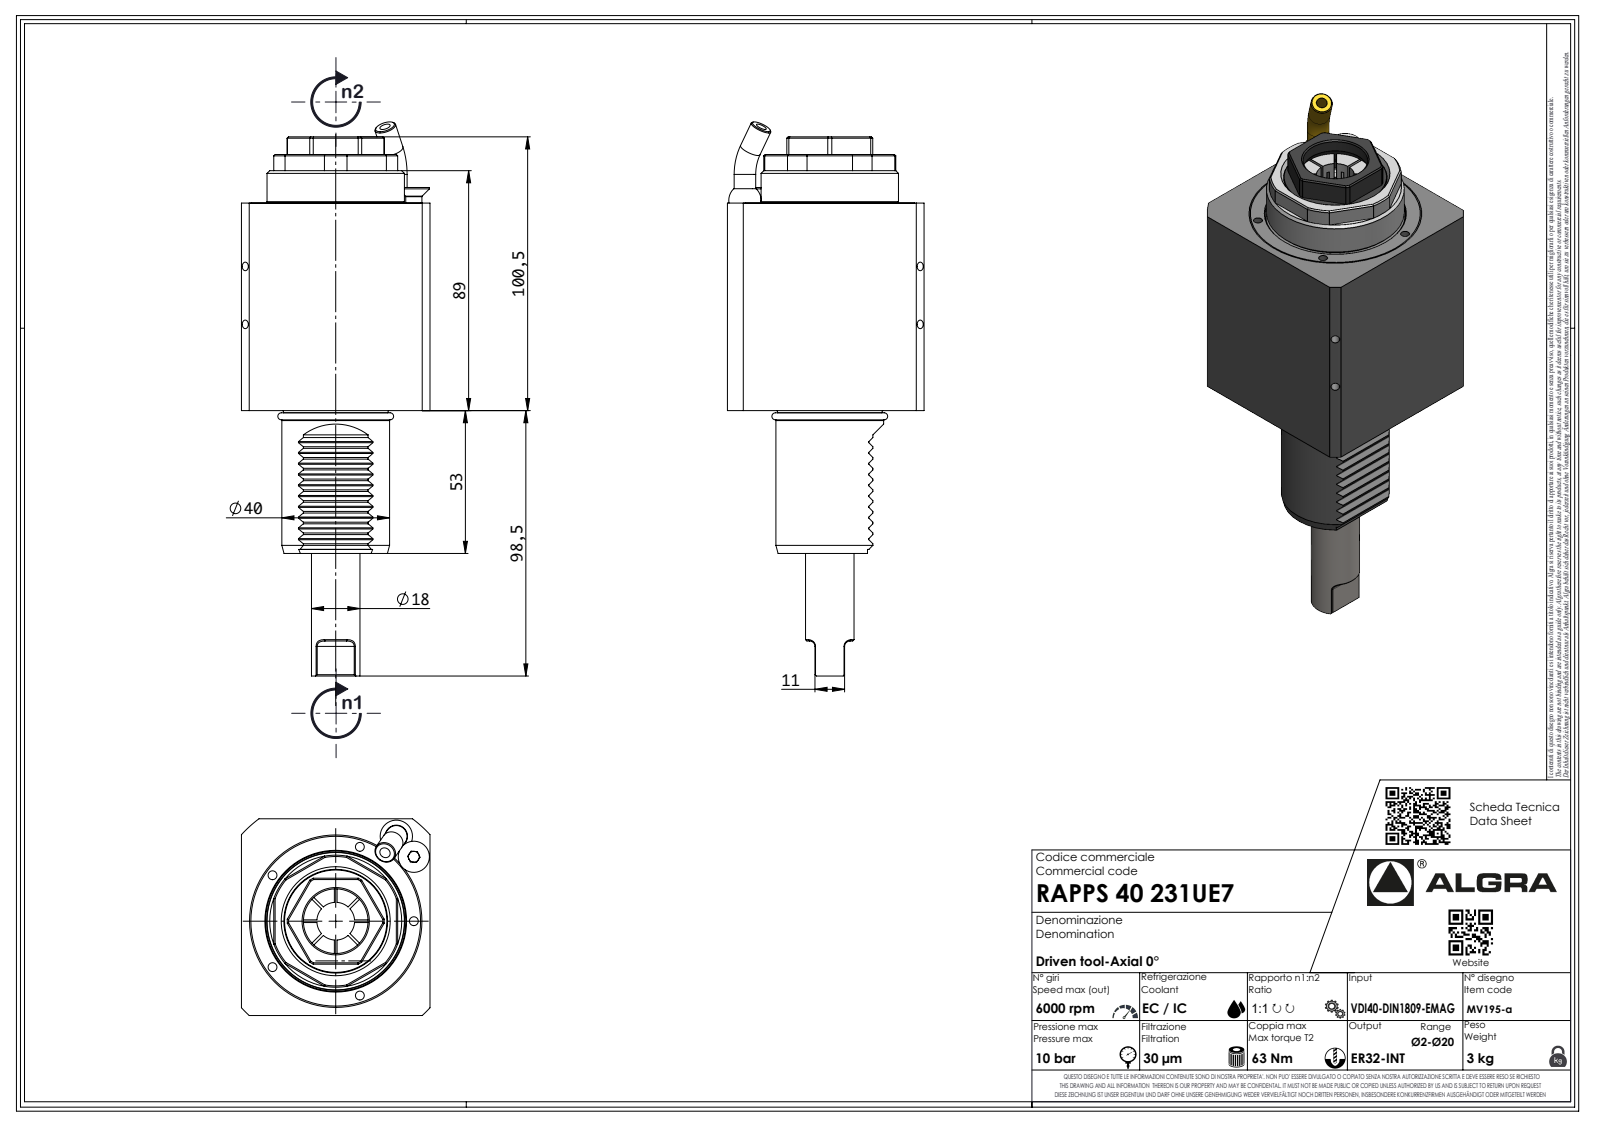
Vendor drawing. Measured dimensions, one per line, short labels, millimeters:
name: RAPPS40231UE7
written by: SolidWorks 2023 (AUTOMOTIVE_DESIGN)
unit: mm
bodies: 1 solid, 446 faces (285 planar, 61 cylindrical, 100 other)
size: 205.6 × 73 × 70
volume: 505 574 mm³; area: 44 996 mm²
holes: 1× ⌀2.1
bosses: 2× ⌀8, 1× ⌀51, 1× ⌀40, 1× ⌀38.7, 1× ⌀18, 1× ⌀6.37, 1× ⌀1.7
rounds: 11× R0.3, 7× R0.33, 7× R0.52, 7× R3.7, 2× R2, 1× R0.21, 1× R18, 1× R24.5
face distances: 70, 73, 77, 77.02, 95.02, 18.02, 18, 6.55, 101.57, 24.57
